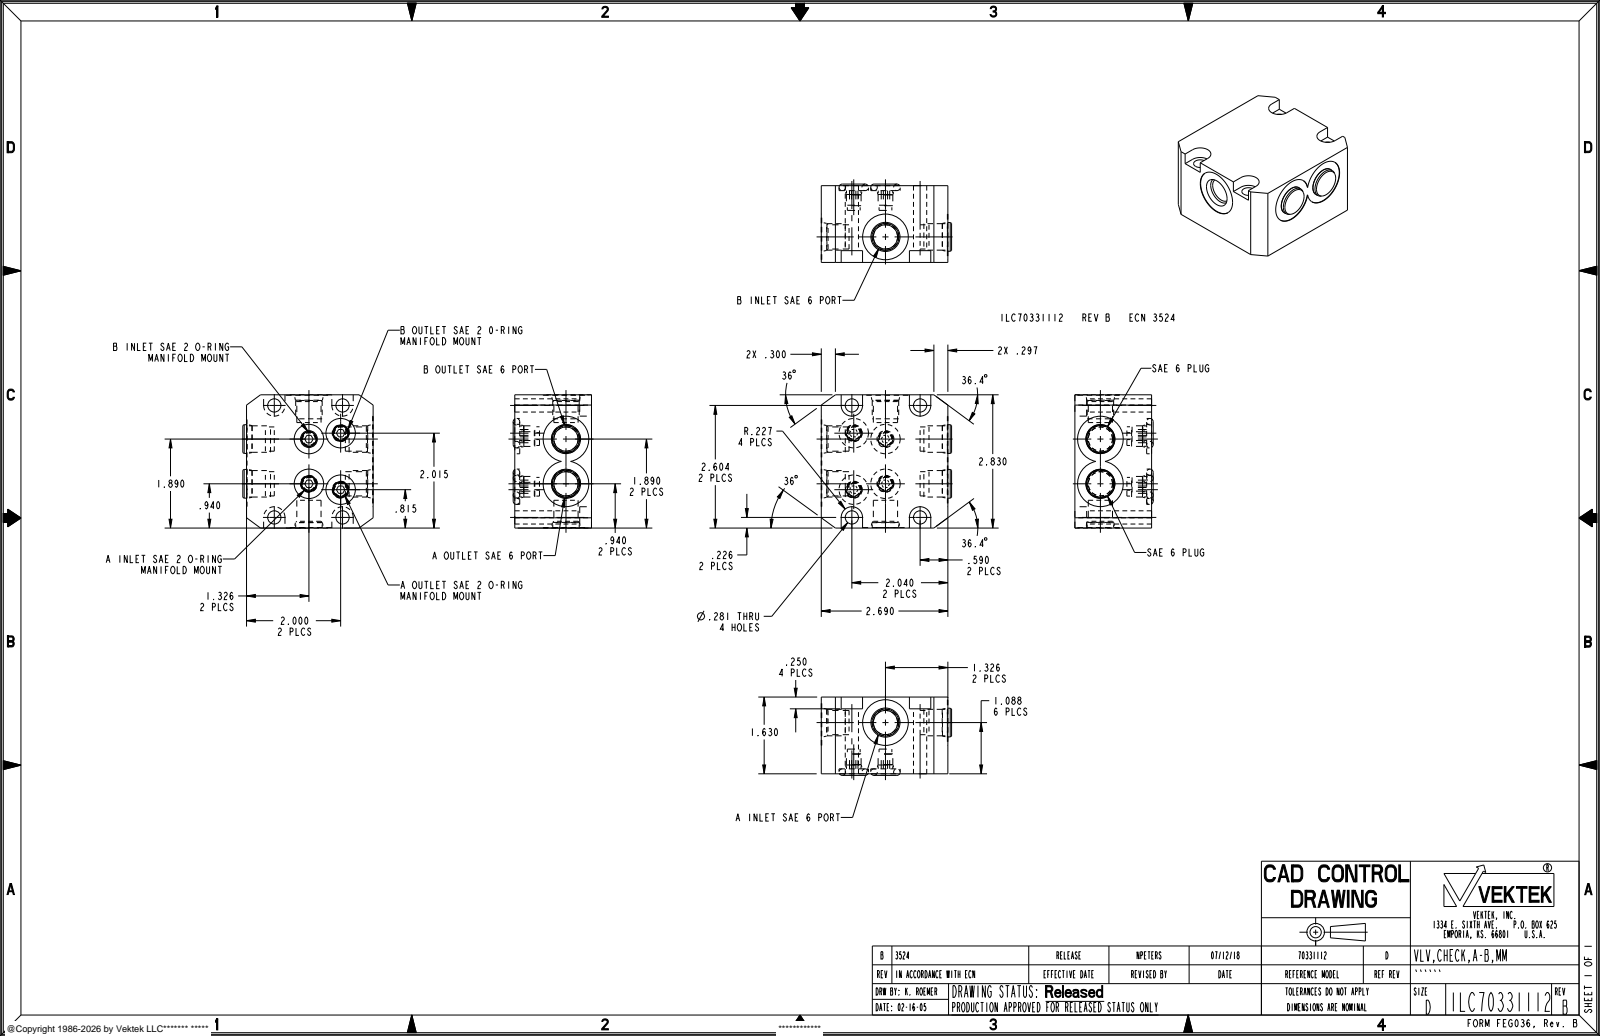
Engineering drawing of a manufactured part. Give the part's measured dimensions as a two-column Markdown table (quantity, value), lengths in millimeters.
| quantity | value |
| --- | --- |
| part name | ILC70331112 |
| STEP written by | PRO/ENGINEER BY PARAMETRIC TECHNOLOGY CORPORATION, 2013320 (AUTOMOTIVE_DESIGN) |
| units | millimeters |
| bodies | 4 solids, 227 faces (87 planar, 84 cylindrical, 56 other) |
| overall size | 71.9 × 70.3 × 42.3 |
| volume | 179 600 mm³ |
| surface area | 34 280 mm² |
| round holes (diameter × count) | 6.9 × 4, 7.1 × 4, 15.9 × 4, 13.1 × 3, 24.6 × 3 |
| round bosses / shafts (diameter × count) | 8 × 4, 7.8 × 4, 14.3 × 3, 15.5 × 2 |
| partial cylindrical surfaces (radius × count) | 5.8 × 4 |
| main face-to-face distances | 41.4, 71.9, 68.3, 15, 2.7, 38.7, 68.1, 71.6, 67.8, 68.1 |
| hole center spacings | 15, 17.4, 24.1, 25.7, 26.1, 32.2, 36.8, 38.8 |
